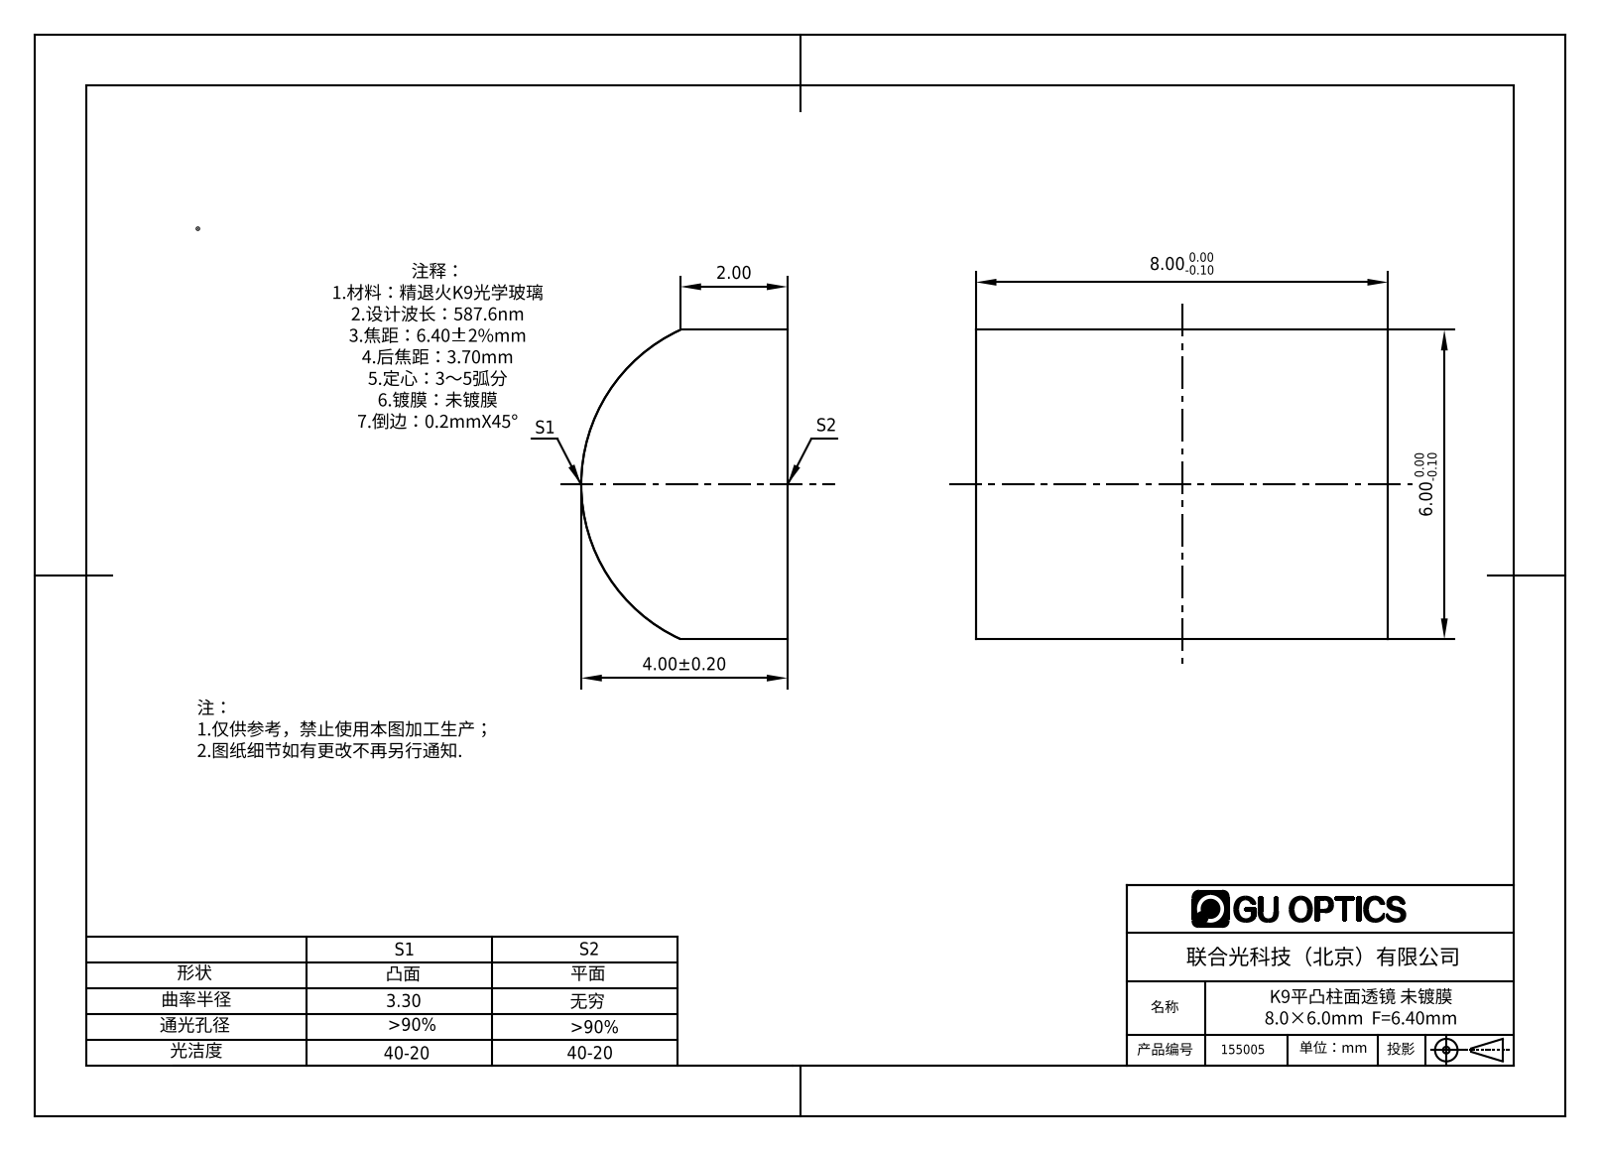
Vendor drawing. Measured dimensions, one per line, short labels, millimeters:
name: 155005
written by: SolidWorks 2016 (AUTOMOTIVE_DESIGN)
unit: mm
bodies: 1 solid, 6 faces (5 planar, 1 cylindrical, 0 other)
size: 8 × 6 × 4
volume: 166 mm³; area: 183 mm²
rounds: 1× R3.3
face distances: 8, 6
